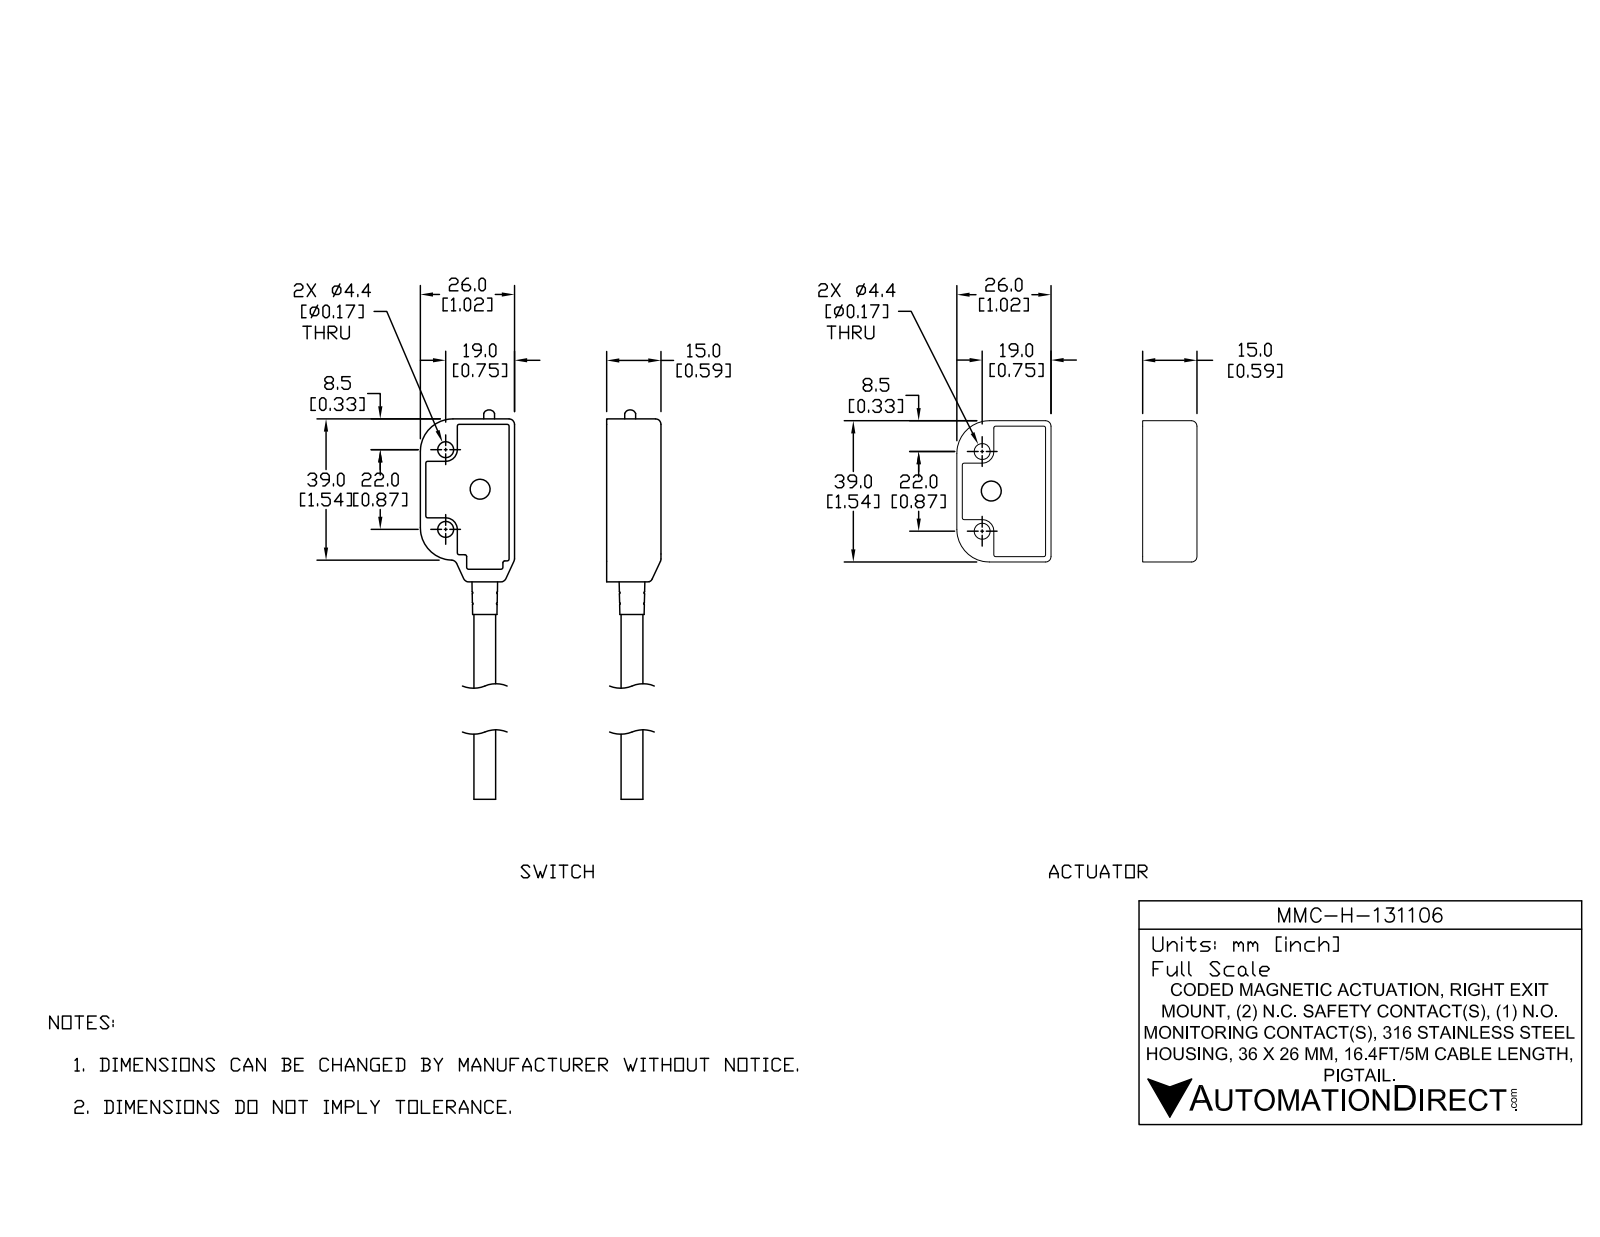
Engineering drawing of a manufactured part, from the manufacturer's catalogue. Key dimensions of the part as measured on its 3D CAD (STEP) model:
Part name (STEP PRODUCT): MMC-H-131106_1; MMC-H-131106_2; MMC-H-131106
STEP written by: SolidWorks 2017 (AUTOMOTIVE_DESIGN)
Units: inches
Bodies: 9 solids, 599 faces (178 planar, 232 cylindrical, 189 other)
Overall size (bounding box): 7.902 × 2.087 × 0.591
Volume: 1.233 in³ · Surface area: 31 in²
Round holes (diameter × count): ⌀0.173 ×4, ⌀0.197 ×2, ⌀0.118 ×1, ⌀0.232 ×1, ⌀0.283 ×1
Round bosses / shafts (diameter × count): ⌀0.079 ×2, ⌀0.031 ×2, ⌀0.339 ×1, ⌀0.299 ×1, ⌀0.28 ×1, ⌀0.236 ×1, ⌀0.157 ×1
Partial cylindrical surfaces — rounded edges, fillets, slot ends (radius × count): R0.02 ×82, R0.012 ×26, R0.059 ×15, R0.008 ×8, R0.157 ×6, R0.126 ×4, R0.13 ×4, R0.181 ×4
Main face-to-face distances: 0.059, 0.575, 0.516, 0.098, 0.461, 0.52, 0.055, 0.591, 0.531, 0.965
Hole centre spacings: 0.866, 1.535, 1.763, 0.076, 0.44, 0.448, 0.569, 0.575
